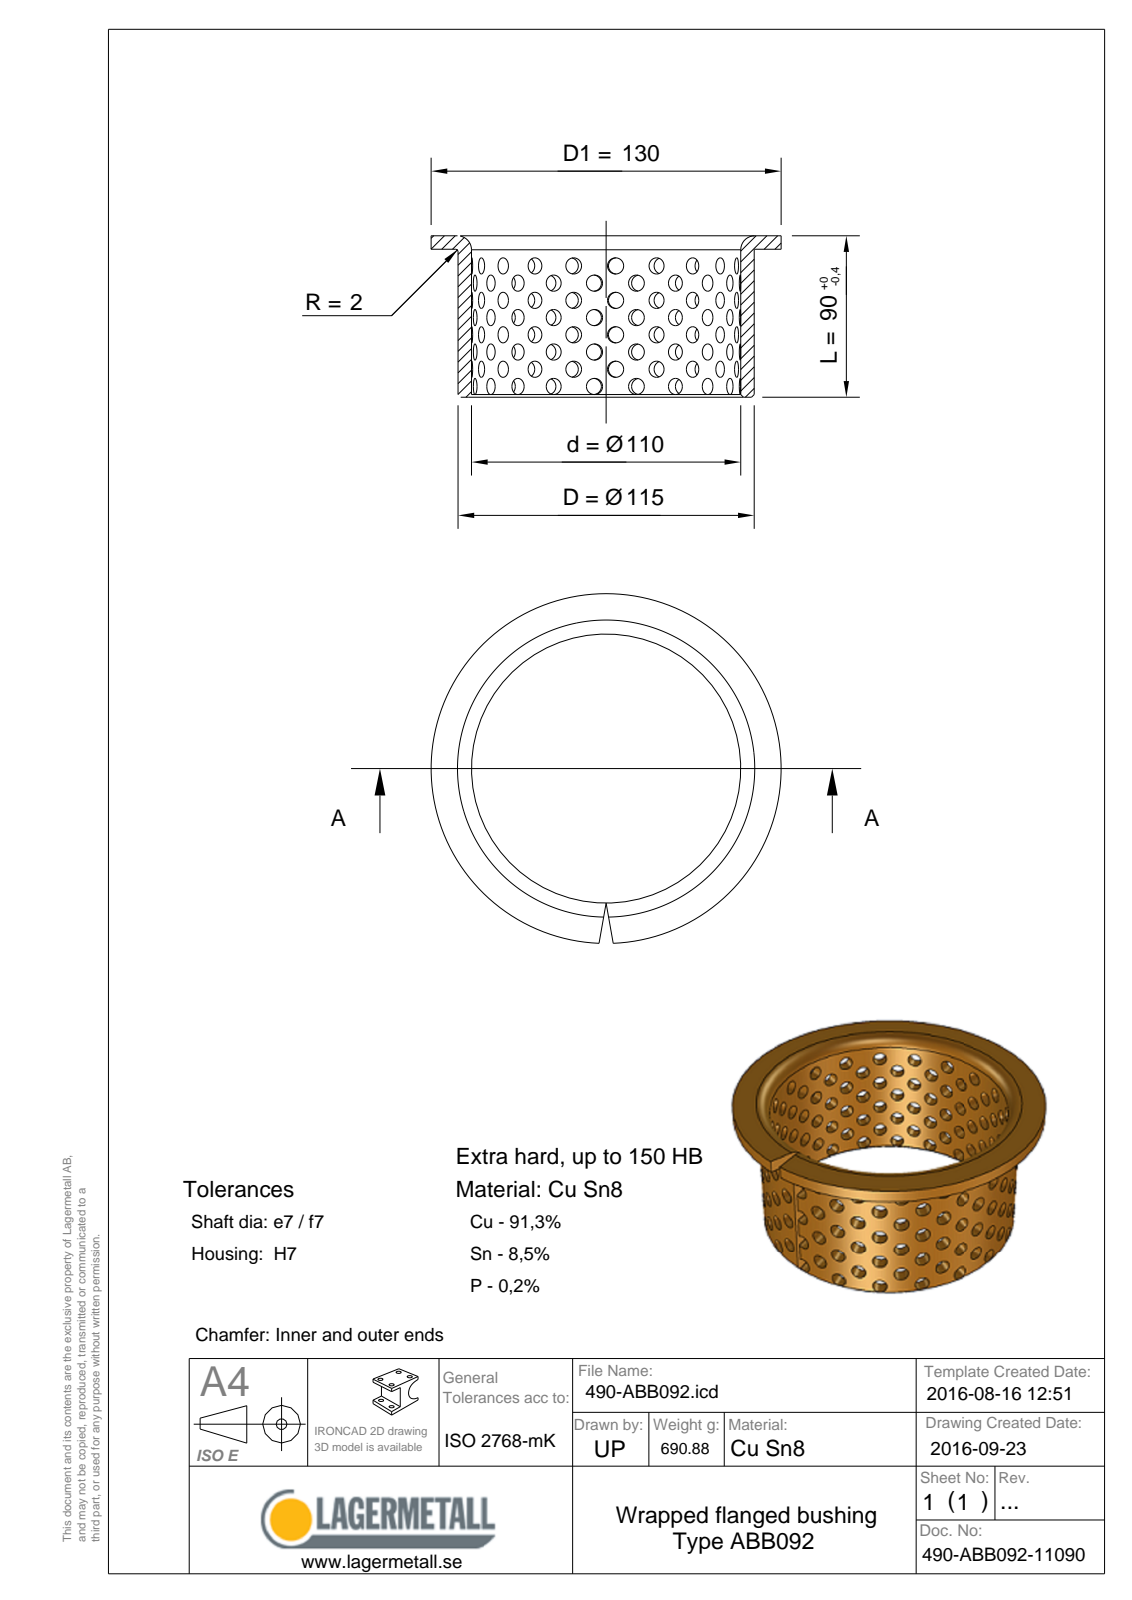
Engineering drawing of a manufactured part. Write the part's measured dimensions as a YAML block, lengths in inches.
step_written_by: "Spatial InterOp 3D (CONFIG_CONTROL_DESIGN)"
units: inches
bodies: {solids: 1, faces: 26, planar: 5, cylindrical: 9, other: 12}
overall_size: [5.118, 5.118, 3.543]
volume: 5.205
surface_area: 109.2
round_holes:
  - {diameter: 4.331, count: 1}
round_bosses_or_shafts:
  - {diameter: 5.118, count: 1}
  - {diameter: 4.528, count: 1}
face_to_face_distances: [0.098, 3.445, 3.543]
